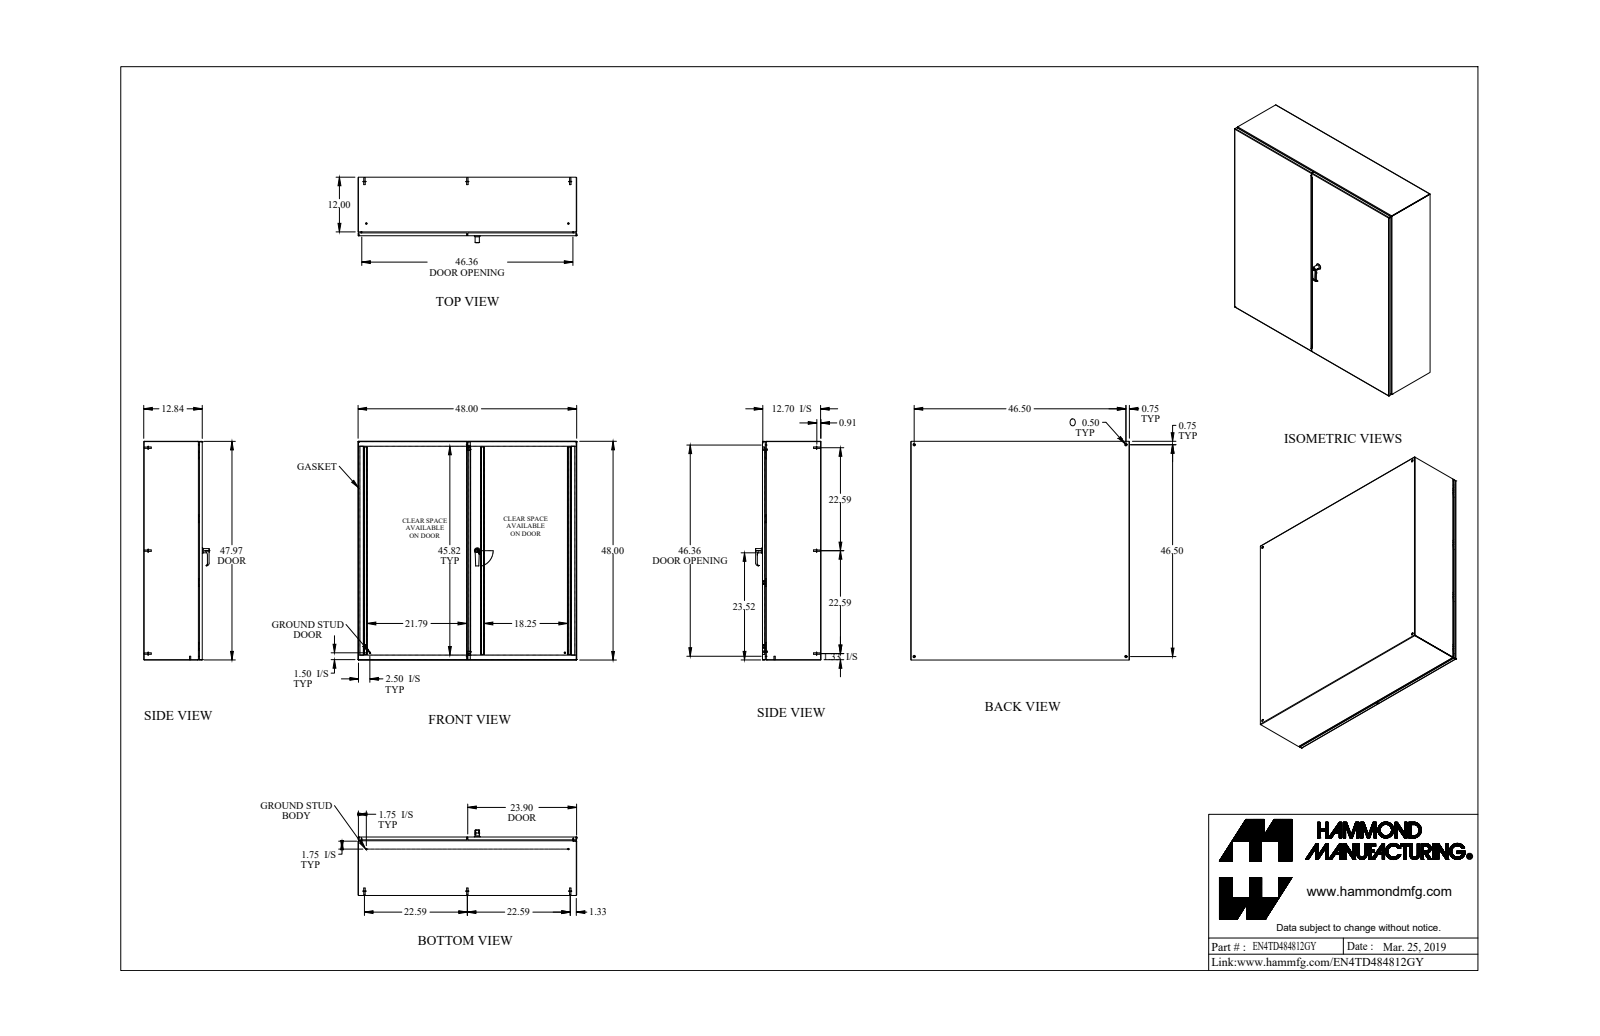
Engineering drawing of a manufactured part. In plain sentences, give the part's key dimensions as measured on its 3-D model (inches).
The part is named "EN4TD484812GY". Its 3-D file was written by "SolidWorks 2018 (AUTOMOTIVE_DESIGN)". It is 97 solids with 2415 faces: 1058 planar, 882 cylindrical and 475 other. Overall it measures 48 by 48 by 14.372 inches. Its volume is 599.8 cubic inches and its surface area 15 981 square inches. Round holes: 6 of diameter 0.196, 4 of diameter 0.176, 4 of diameter 0.5, 3 of diameter 0.24, 3 of diameter 0.242, 3 of diameter 0.25, 3 of diameter 0.265, 2 of diameter 0.172, 2 of diameter 0.256, 2 of diameter 0.26, 2 of diameter 0.313, 2 of diameter 0.394. Round bosses or shafts: 12 of diameter 0.25, 10 of diameter 0.313, 8 of diameter 0.625, 8 of diameter 0.27, 4 of diameter 0.51, 4 of diameter 0.375, 4 of diameter 0.281, 4 of diameter 0.156. Partial cylindrical surfaces (rounded edges, fillets, slot ends): 26 of radius 0.036, 26 of radius 0.108, 24 of radius 0.063, 20 of radius 0.094, 18 of radius 0.043, 18 of radius 0.081, 16 of radius 0.006, 16 of radius 0.02. The main face-to-face distances are 0.072, 12.77, 12.698, 12.842, 47.928, 48, 0.072, 47.856, 47.856, 47.928. The hole center spacings are 46.5, 0.787, 18.094, 20.797, 25.754, 28.447, 31.385, 34.448.
